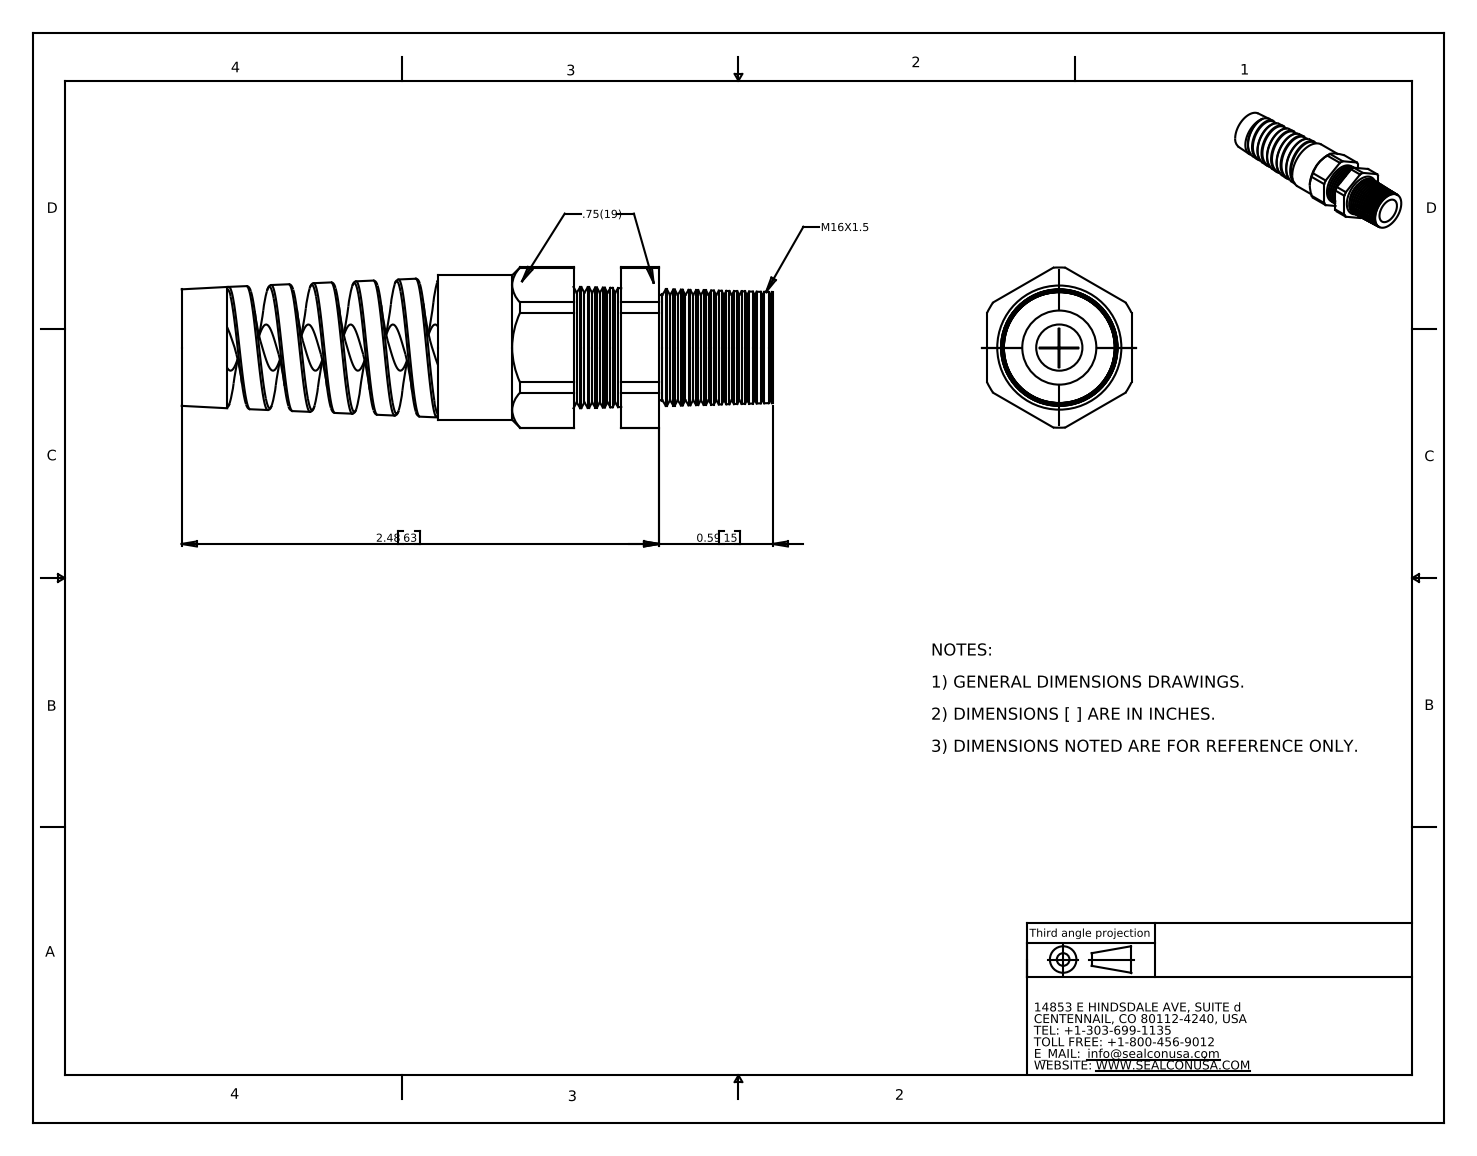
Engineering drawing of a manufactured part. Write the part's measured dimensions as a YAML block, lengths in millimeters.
part_name: "CF16DR-GY"
step_written_by: "SolidWorks 2007 (CONFIG_CONTROL_DESIGN)"
units: millimeters
bodies: {solids: 2, faces: 220, planar: 25, cylindrical: 35, other: 160}
overall_size: [78, 21.2, 19.1]
volume: 13100
surface_area: 8890
round_holes:
  - {diameter: 6.1, count: 1}
  - {diameter: 6.7, count: 1}
round_bosses_or_shafts:
  - {diameter: 19.1, count: 1}
  - {diameter: 13.9, count: 1}
partial_cylinders:
  - {radius: 10.6, count: 1}
face_to_face_distances: [19.1, 43.6, 58, 14.4, 33.8, 9.8, 24.2, 19.1, 41.4, 7.6]
